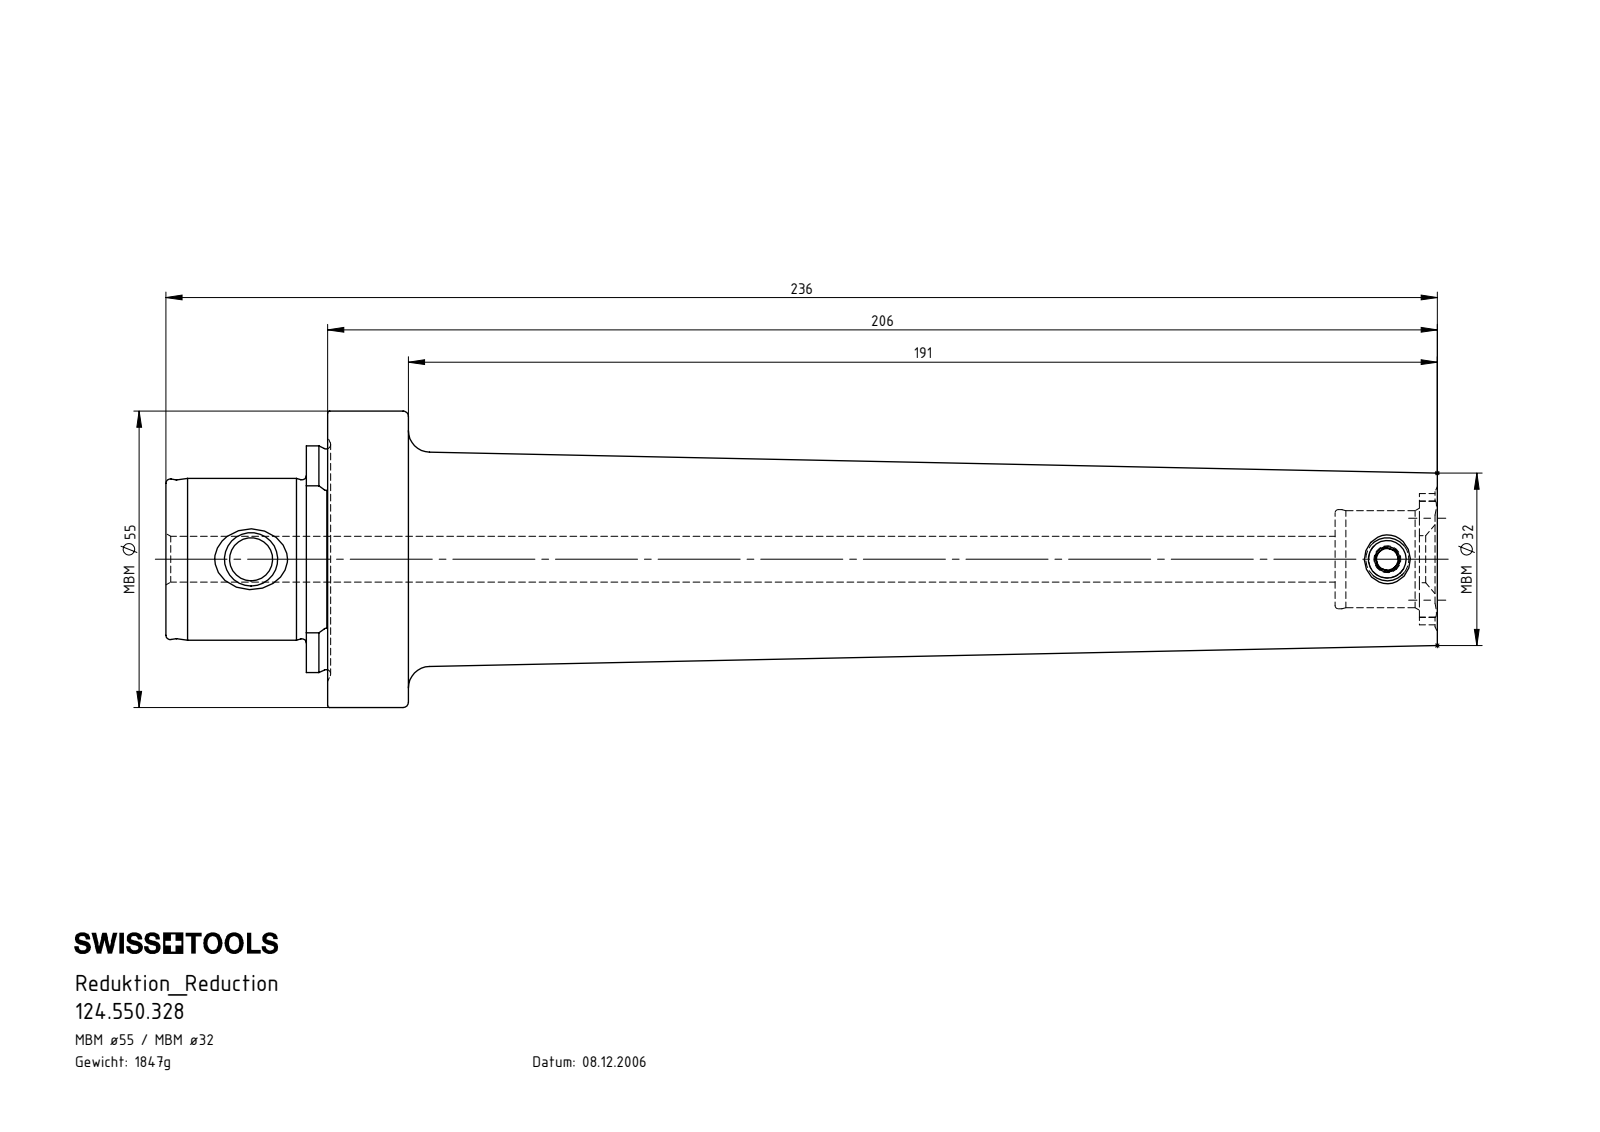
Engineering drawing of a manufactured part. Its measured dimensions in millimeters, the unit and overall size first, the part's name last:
Units: millimetres
Overall size (bounding box): 236 × 55 × 55
Round holes (diameter × count): ⌀4 ×1, ⌀7 ×1, ⌀8 ×1, ⌀8.5 ×1, ⌀18 ×1, ⌀18.4 ×1
Round bosses / shafts (diameter × count): ⌀55 ×1, ⌀30 ×1, ⌀8 ×1
Partial cylindrical surfaces — rounded edges, fillets, slot ends (radius × count): R3.2 ×4, R10.5 ×1, R12.18 ×1, R21.02 ×1
Main face-to-face distances: 30, 26.05, 3.95, 45, 18.95, 15, 236, 209.95, 206, 191
Hole centre spacings: 210.9
Volume: 235 224 mm³ · Surface area: 38 510 mm²
Bodies: 2 solids, 134 faces (33 planar, 32 cylindrical, 69 other)
Part name (STEP PRODUCT): MB3-ER1.001.011_A; MB5-MB3.K01.206_C; 124.550.328
STEP written by: SolidWorks 2017 (CONFIG_CONTROL_DESIGN)
